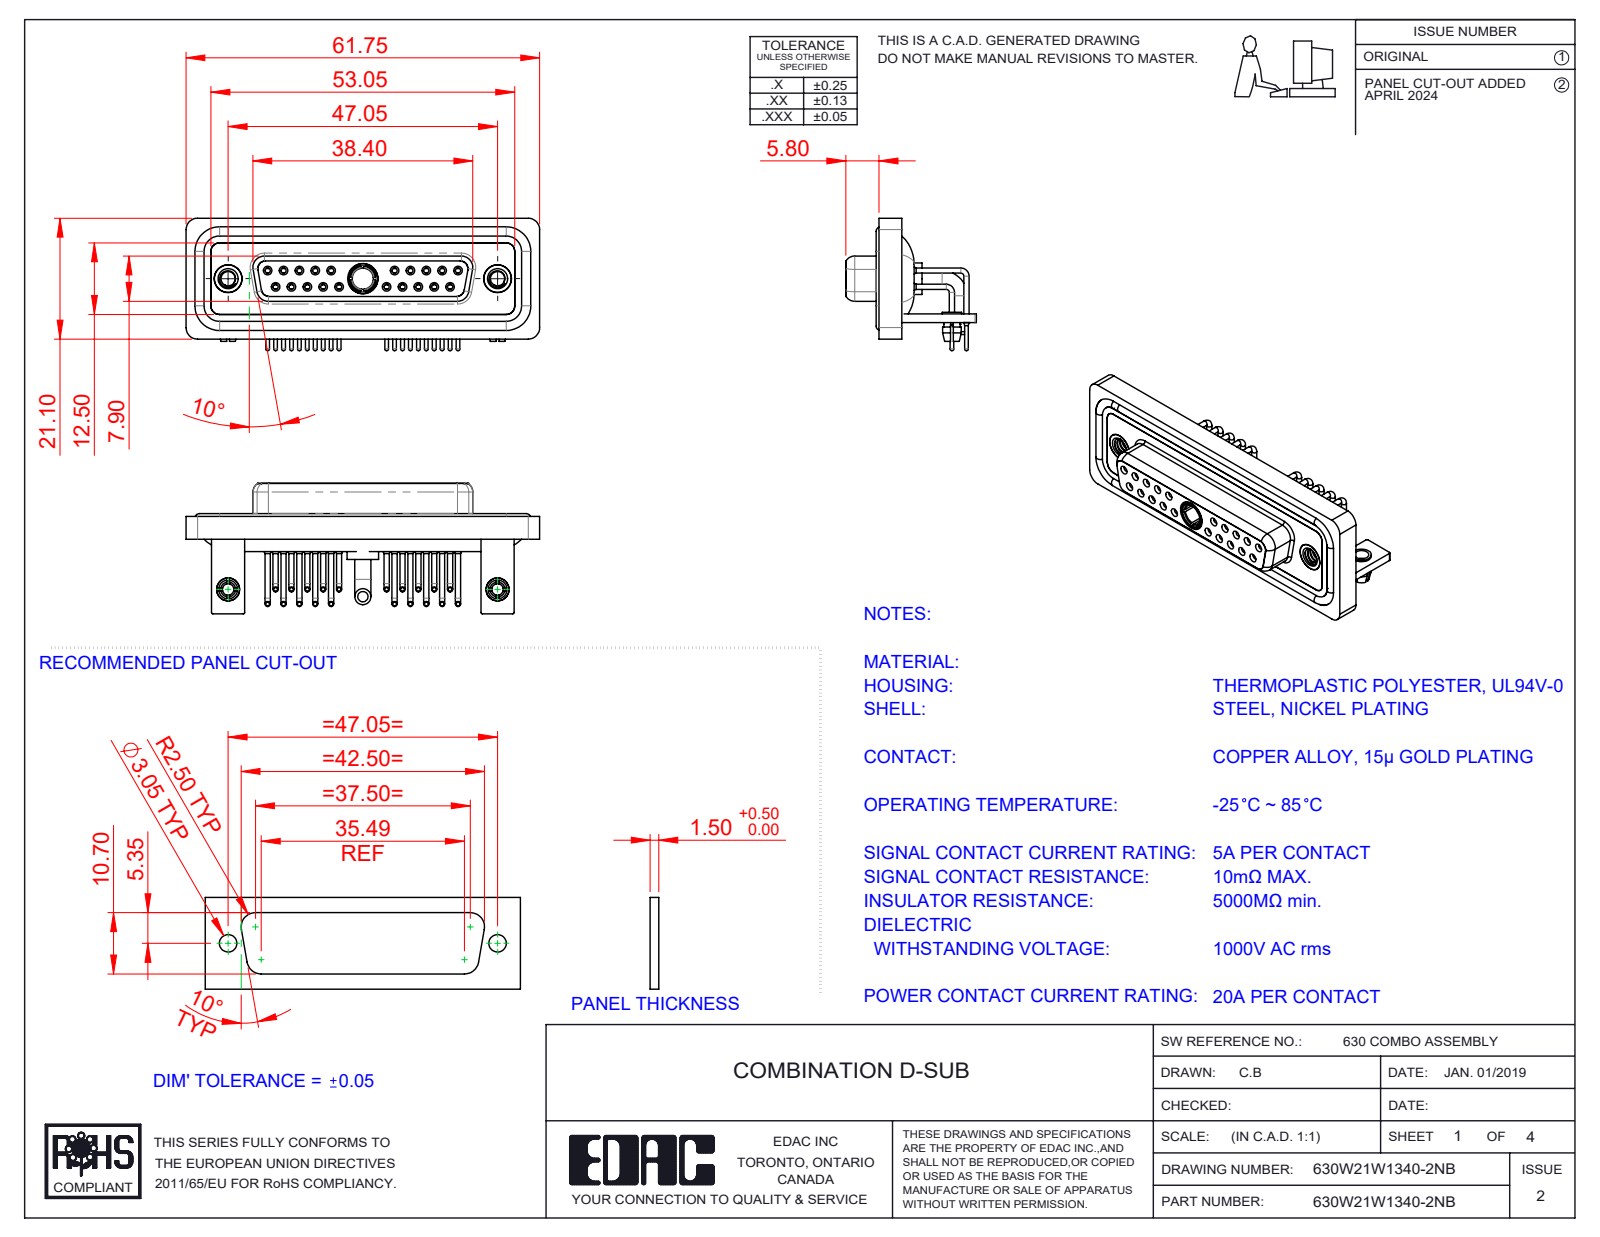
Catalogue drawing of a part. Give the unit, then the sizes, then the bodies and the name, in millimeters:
Units: millimetres
Overall size (bounding box): 61.75 × 23.12 × 22.8
Round holes (diameter × count): ⌀2 ×22, ⌀0.9 ×20, ⌀1.1 ×20, ⌀1.5 ×20, ⌀1.6 ×10, ⌀1.7 ×10, ⌀2.5 ×4, ⌀4.85 ×3, ⌀3.2 ×2, ⌀4 ×2, ⌀4.05 ×2, ⌀5 ×2
Round bosses / shafts (diameter × count): ⌀0.9 ×20, ⌀0.65 ×20, ⌀1.6 ×14, ⌀4.95 ×2, ⌀4.8 ×2, ⌀4 ×2, ⌀3.4 ×2, ⌀3.3 ×2
Partial cylindrical surfaces — rounded edges, fillets, slot ends (radius × count): R2 ×19, R1.5 ×18, R0.25 ×16, R1.35 ×8, R1.6 ×8, R0.5 ×5, R0.6 ×4, R0.65 ×4
Main face-to-face distances: 0.4, 1.8, 2.9, 3.7, 1.5, 4.1, 1.1, 1.4, 1.6, 2.5
Hole centre spacings: 3.16, 2.77, 5.54, 8.31, 5.04, 19.39, 20.97, 22.16
Volume: 8 901 mm³ · Surface area: 15 729 mm²
Bodies: 33 solids, 1658 faces (502 planar, 727 cylindrical, 429 other)
Part name (STEP PRODUCT): 630Combo Threaded Rivet_A; 630Combo Shell Rear_25 Contacts; Power Socket_20A RA; 630W21W1340-2NB (+7 more)
STEP written by: SolidWorks 2023 (CONFIG_CONTROL_DESIGN)
